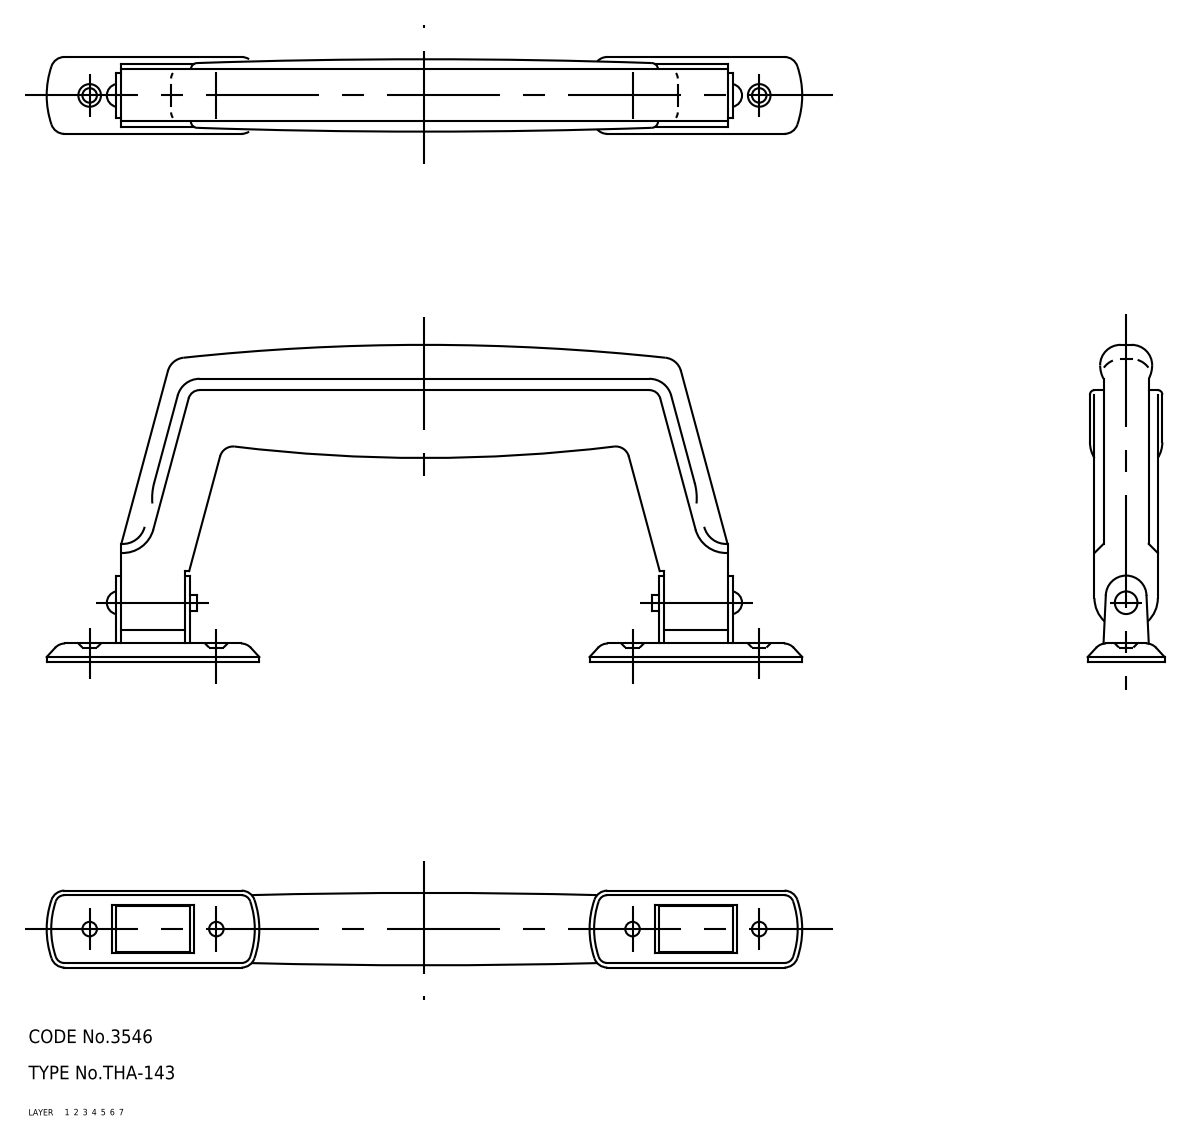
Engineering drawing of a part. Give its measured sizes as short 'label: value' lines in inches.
name: joint; pin; bracket; grip (+1 more)
written by: CADfix (AUTOMOTIVE_DESIGN)
unit: in
bodies: 7 solids, 356 faces (0 planar, 0 cylindrical, 356 other)
size: 6.575 × 2.756 × 0.669
volume: 3.123 in³; area: 31.61 in²
